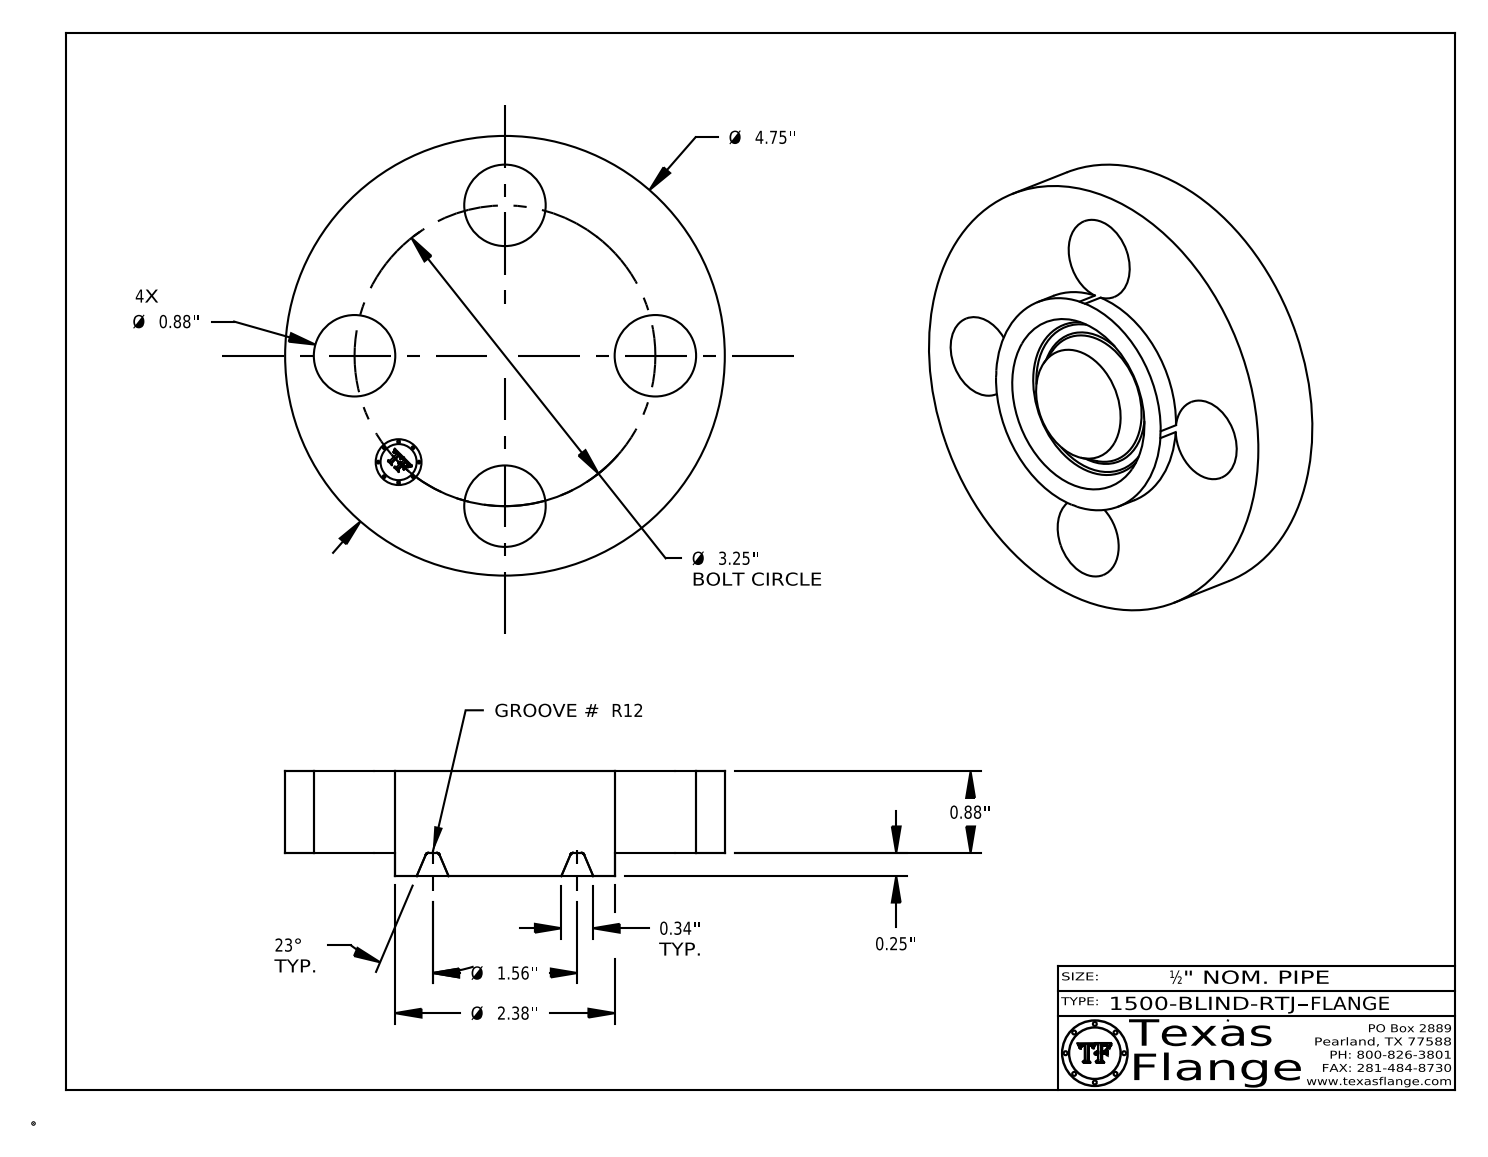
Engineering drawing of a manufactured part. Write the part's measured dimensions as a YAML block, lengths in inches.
part_name: "1500-BLIND-RTJ"
step_written_by: "CATIA V5 STEP AP214 (AUTOMOTIVE_DESIGN)"
units: inches
bodies: {solids: 1, faces: 414, planar: 370, cylindrical: 36, other: 8}
overall_size: [4.75, 4.75, 1.13]
volume: 14.27
surface_area: 56.98
round_holes:
  - {diameter: 0.88, count: 4}
  - {diameter: 0.495, count: 1}
round_bosses_or_shafts:
  - {diameter: 0.03, count: 8}
  - {diameter: 4.75, count: 1}
  - {diameter: 2.375, count: 1}
  - {diameter: 0.39, count: 1}
face_to_face_distances: [0.88, 0.25, 1.13, 1.115, 0.865, 0.015, 0.148, 0.144, 0.027, 0.096]
hole_center_spacings: [2.298, 1.244, 3.003, 3.25]
